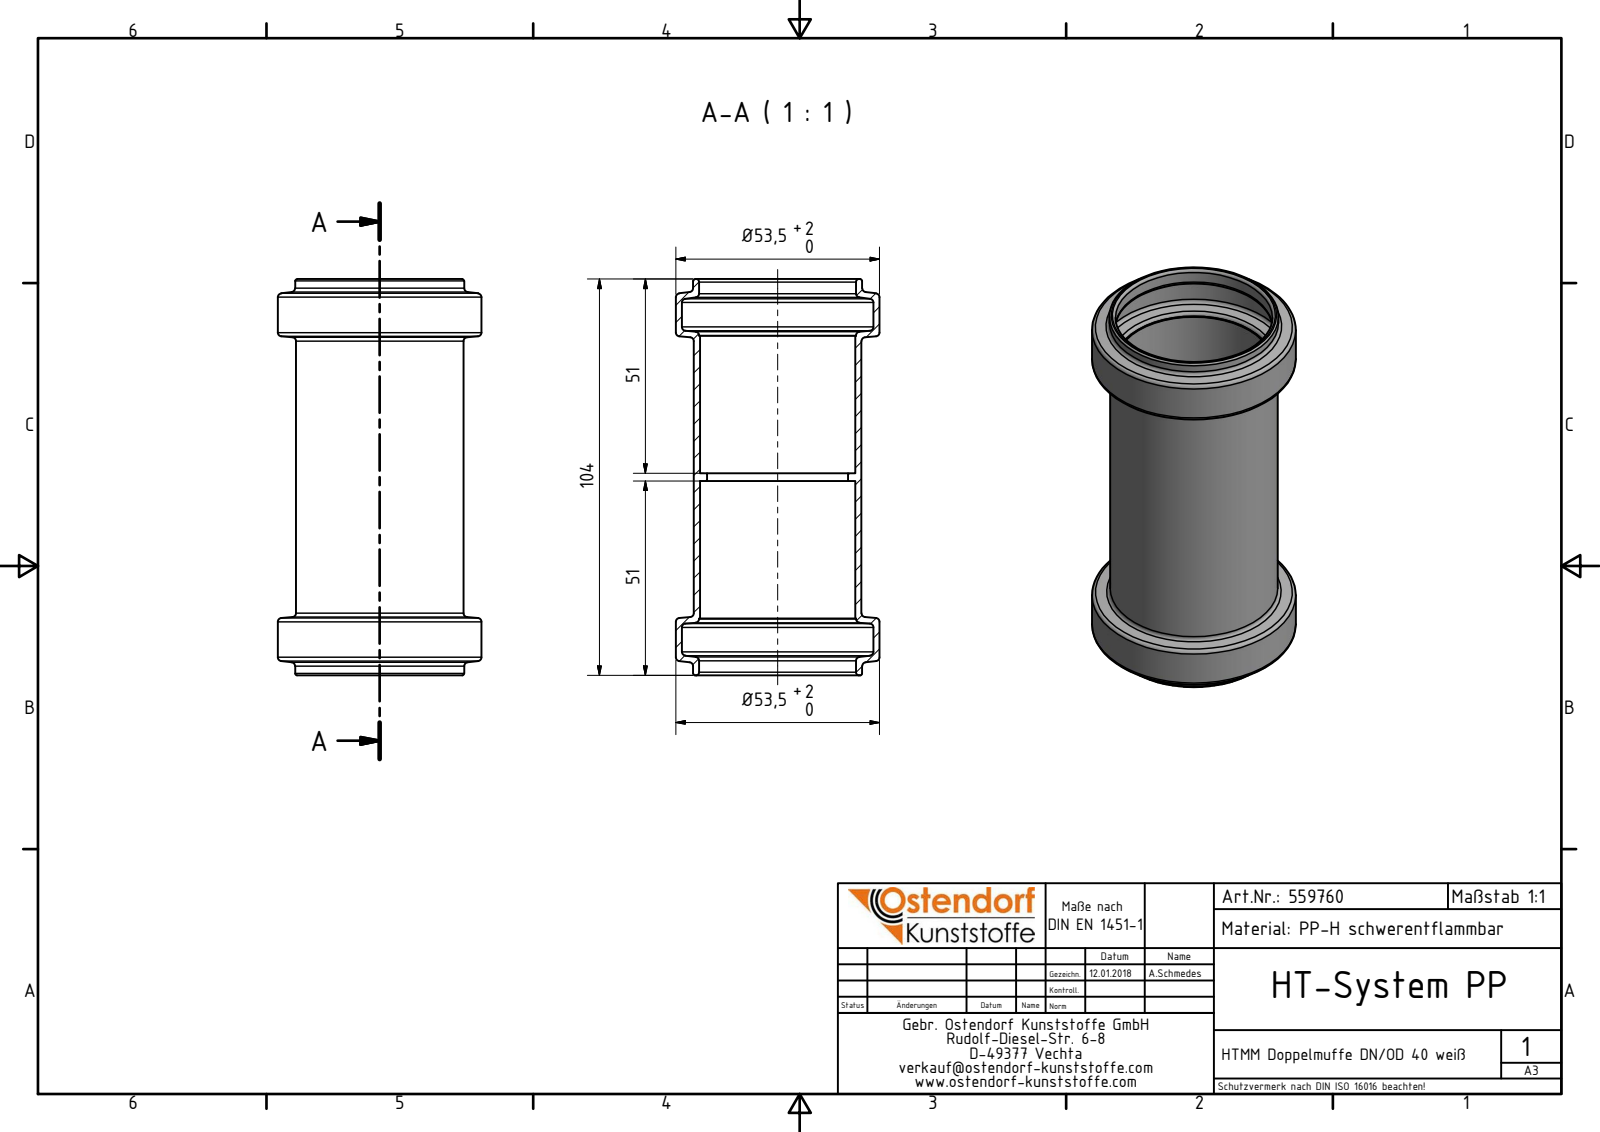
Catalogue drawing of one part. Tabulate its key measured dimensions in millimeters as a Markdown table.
| quantity | value |
| --- | --- |
| part name | 559760 HTMM DN_OD 40 weiß |
| STEP written by | Autodesk Inventor 2016 (AUTOMOTIVE_DESIGN) |
| units | millimeters |
| bodies | 1 solid, 48 faces (6 planar, 14 cylindrical, 28 other) |
| overall size | 104 × 53.5 × 53.5 |
| volume | 27 493 mm³ |
| surface area | 33 846 mm² |
| round holes (diameter × count) | 37 × 1, 40.8 × 1, 41.2 × 1, 50.3 × 1 |
| round bosses / shafts (diameter × count) | 53.5 × 1, 44.4 × 1, 44 × 1 |
| main face-to-face distances | 2, 51, 53, 14.9, 89.1, 36.1, 38.1, 104, 74.2 |
